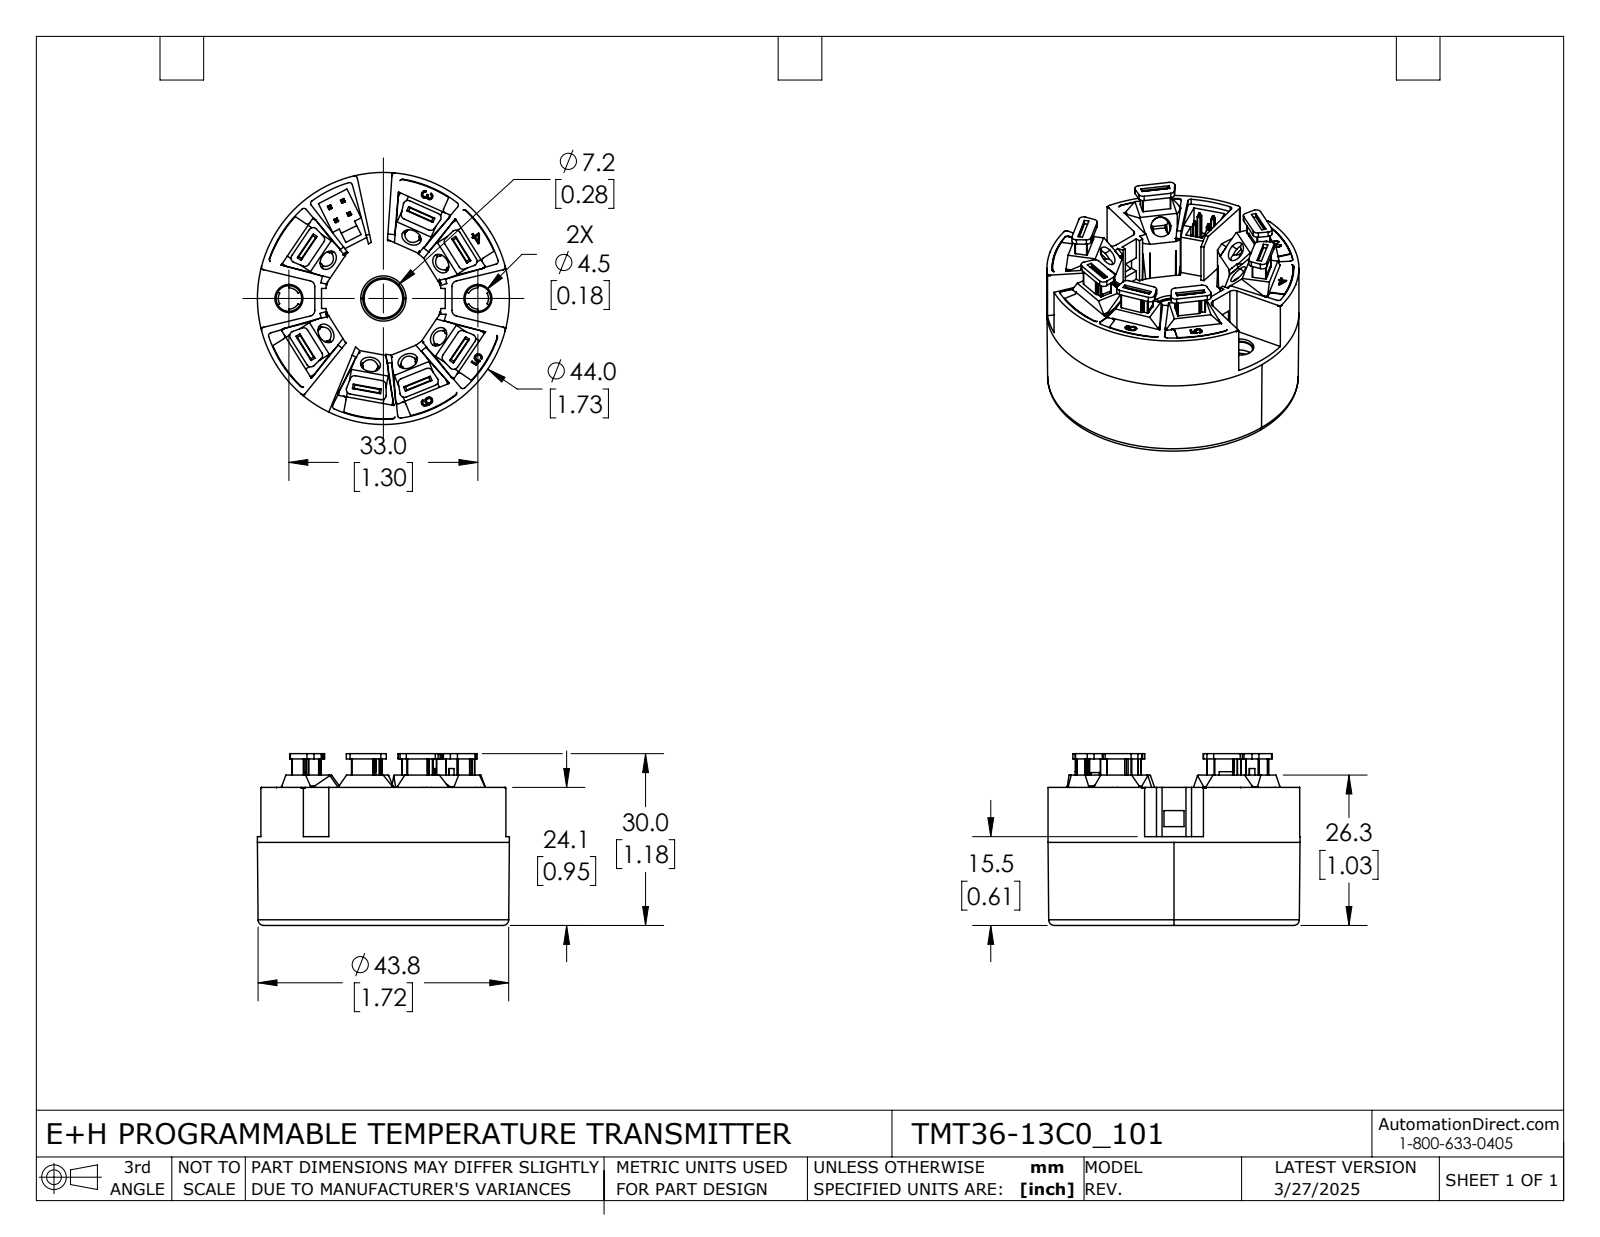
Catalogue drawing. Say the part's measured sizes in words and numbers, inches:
The part is named "TMT36-13C0_101". Its 3-D file was written by "SolidWorks 2021 (AUTOMOTIVE_DESIGN)". It is 1 solid with 1153 faces: 610 planar, 299 cylindrical and 244 other. Overall it measures 1.732 by 1.732 by 1.181 inches. Its volume is 1.832 cubic inches and its surface area 23.56 square inches. Round holes: 7 of diameter 0.138, 2 of diameter 0.193, 1 of diameter 0.213, 1 of diameter 0.283, 1 of diameter 1.646. Round bosses or shafts: 1 of diameter 1.732, 1 of diameter 1.644. Partial cylindrical surfaces (rounded edges, fillets, slot ends): 83 of radius 0.004, 39 of radius 0.02, 28 of radius 0.031, 27 of radius 0.012, 14 of radius 0.008, 11 of radius 0.039, 7 of radius 0.868, 2 of radius 0.073. The main face-to-face distances are 0.059, 0.02, 0.039, 0.571, 0.551, 0.61, 0.949, 0.909, 0.89, 0.339. The hole center spacings are 0.65, 0.299, 0.529, 0.863, 1.299.
